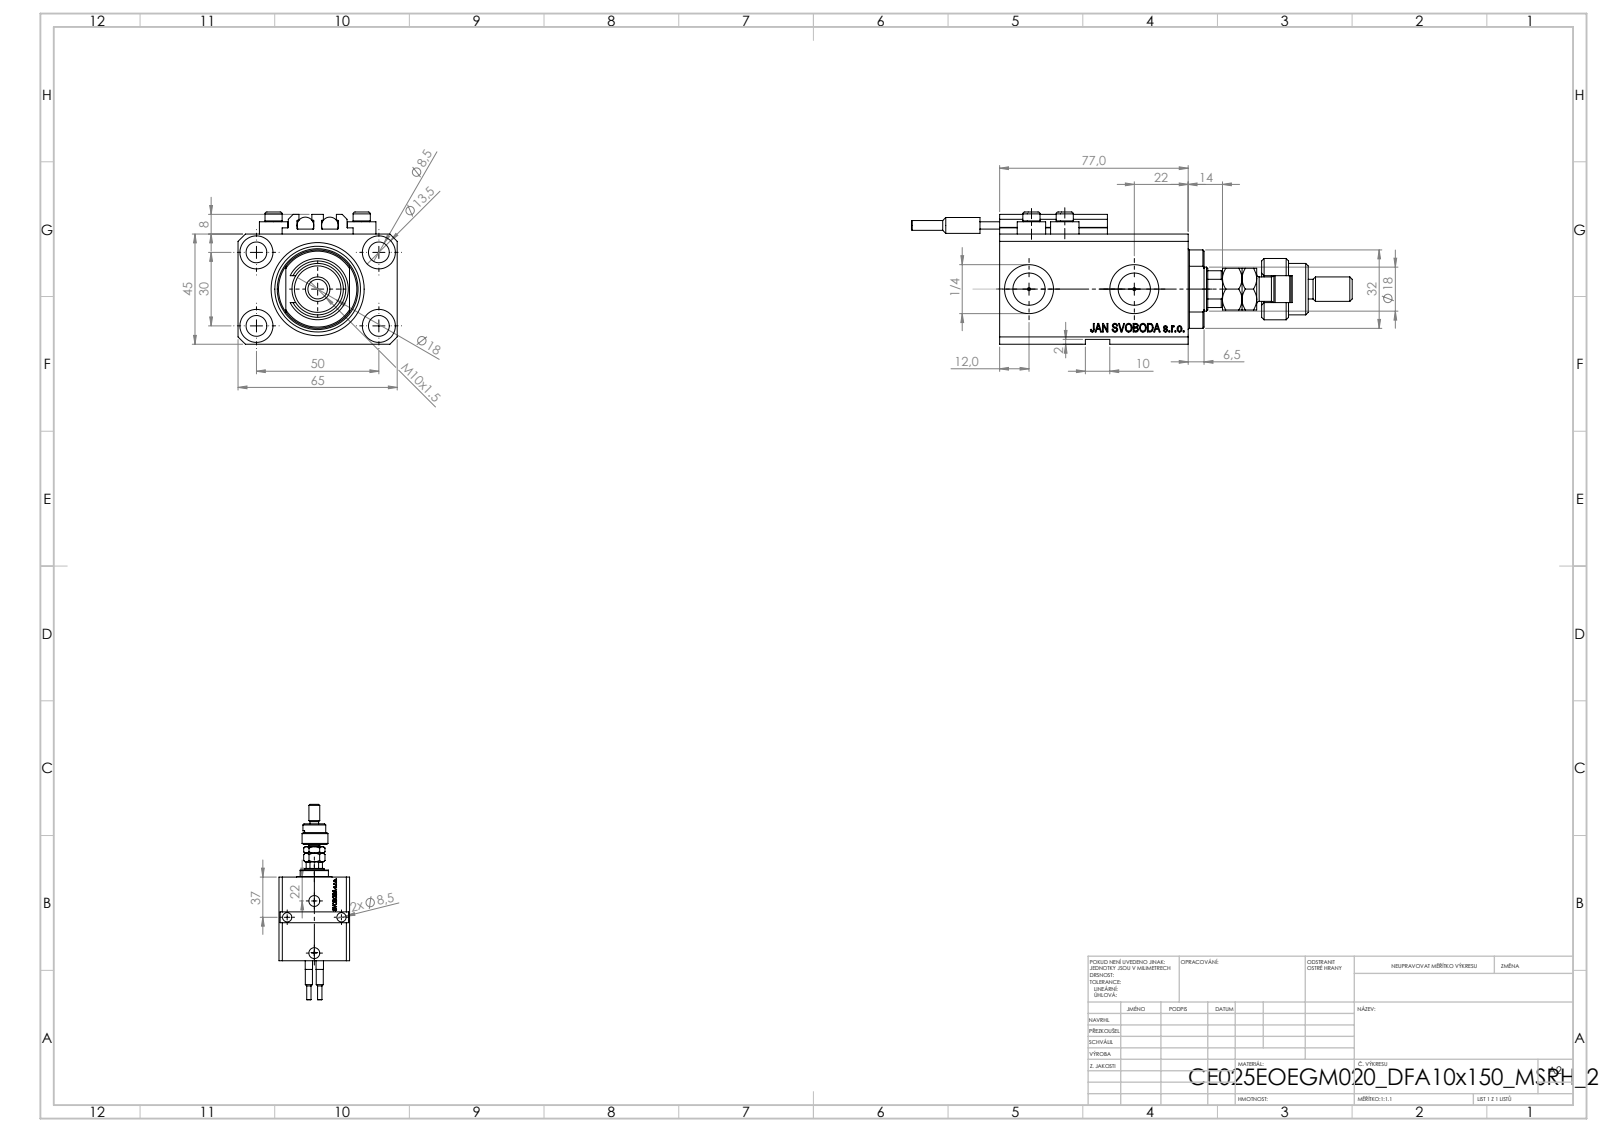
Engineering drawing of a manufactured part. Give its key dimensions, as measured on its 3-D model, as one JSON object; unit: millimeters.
{"part_name": "FEMALE_PART_FOR_DFA; V250CE_C_VCP; V250CE_VC_E; SWITCH_V250CE (+3 more)", "step_written_by": "SolidWorks 2019 (CONFIG_CONTROL_DESIGN)", "units": "millimeters", "bodies": {"solids": 12, "faces": 1204, "planar": 571, "cylindrical": 151, "other": 482}, "overall_size": [180, 65, 54], "volume_mm3": 215142, "surface_area_mm2": 67381, "round_holes": [[8.5, 7], [1.25, 4], [4, 4], [13.5, 4], [10, 2], [13.16, 2], [20, 2], [18, 1], [38, 1]], "round_bosses_or_shafts": [[11.6, 4], [7, 4], [6.8, 2], [6.5, 2], [4, 2], [25, 1], [21, 1], [16, 1]], "partial_cylinders_radius": [[0.2, 10], [5.5, 1], [8.5, 1], [8.75, 1], [16, 1]], "face_to_face_distances": [45, 14, 65, 63, 2, 77, 3, 5, 47, 6.9], "hole_center_spacings": [29.15, 50, 13.6, 15.12, 18.81, 18.97, 26.22, 26.61]}
